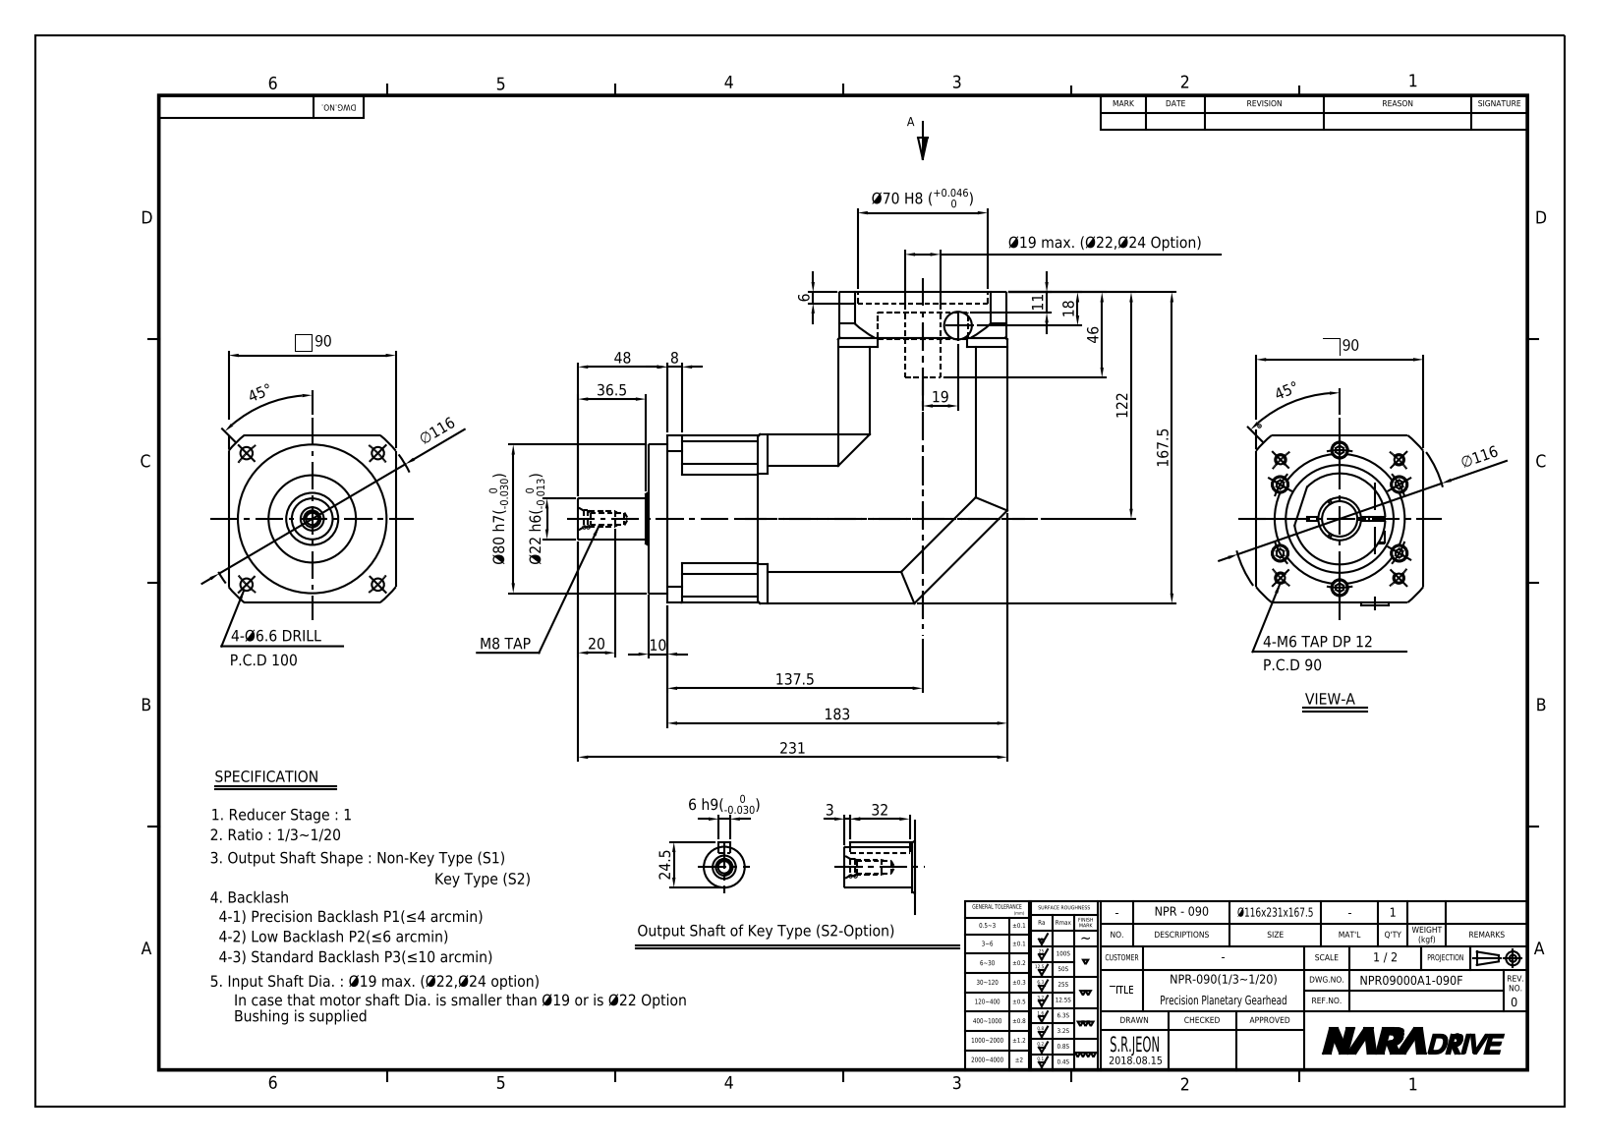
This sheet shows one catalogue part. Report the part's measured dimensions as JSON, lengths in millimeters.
{"part_name": "NPR09000A1-090F-S1", "step_written_by": "Autodesk Inventor 2015 (AUTOMOTIVE_DESIGN)", "units": "millimeters", "bodies": {"solids": 2, "faces": 476, "planar": 241, "cylindrical": 127, "other": 108}, "overall_size": [231, 167.5, 92], "volume_mm3": 1567000, "surface_area_mm2": 167922, "round_holes": [[9, 11], [4.13, 10], [5.5, 10], [4.92, 5], [6.6, 5], [6.65, 1], [7, 1], [8.5, 1], [19, 1], [23, 1], [28, 1], [47, 1]], "round_bosses_or_shafts": [[8.5, 10], [5, 10], [49, 1], [22, 1], [15, 1], [10, 1], [8, 1], [6, 1]], "partial_cylinders_radius": [[0.5, 8], [10, 4], [51.5, 2], [58, 2], [5.5, 1], [35, 1], [51, 1]], "face_to_face_distances": [0.5, 90.5, 91, 90, 51, 142, 104, 38, 89, 104.63], "hole_center_spacings": [37, 45.92, 13.15, 13.32, 32.24, 37.01, 45, 50.32]}
